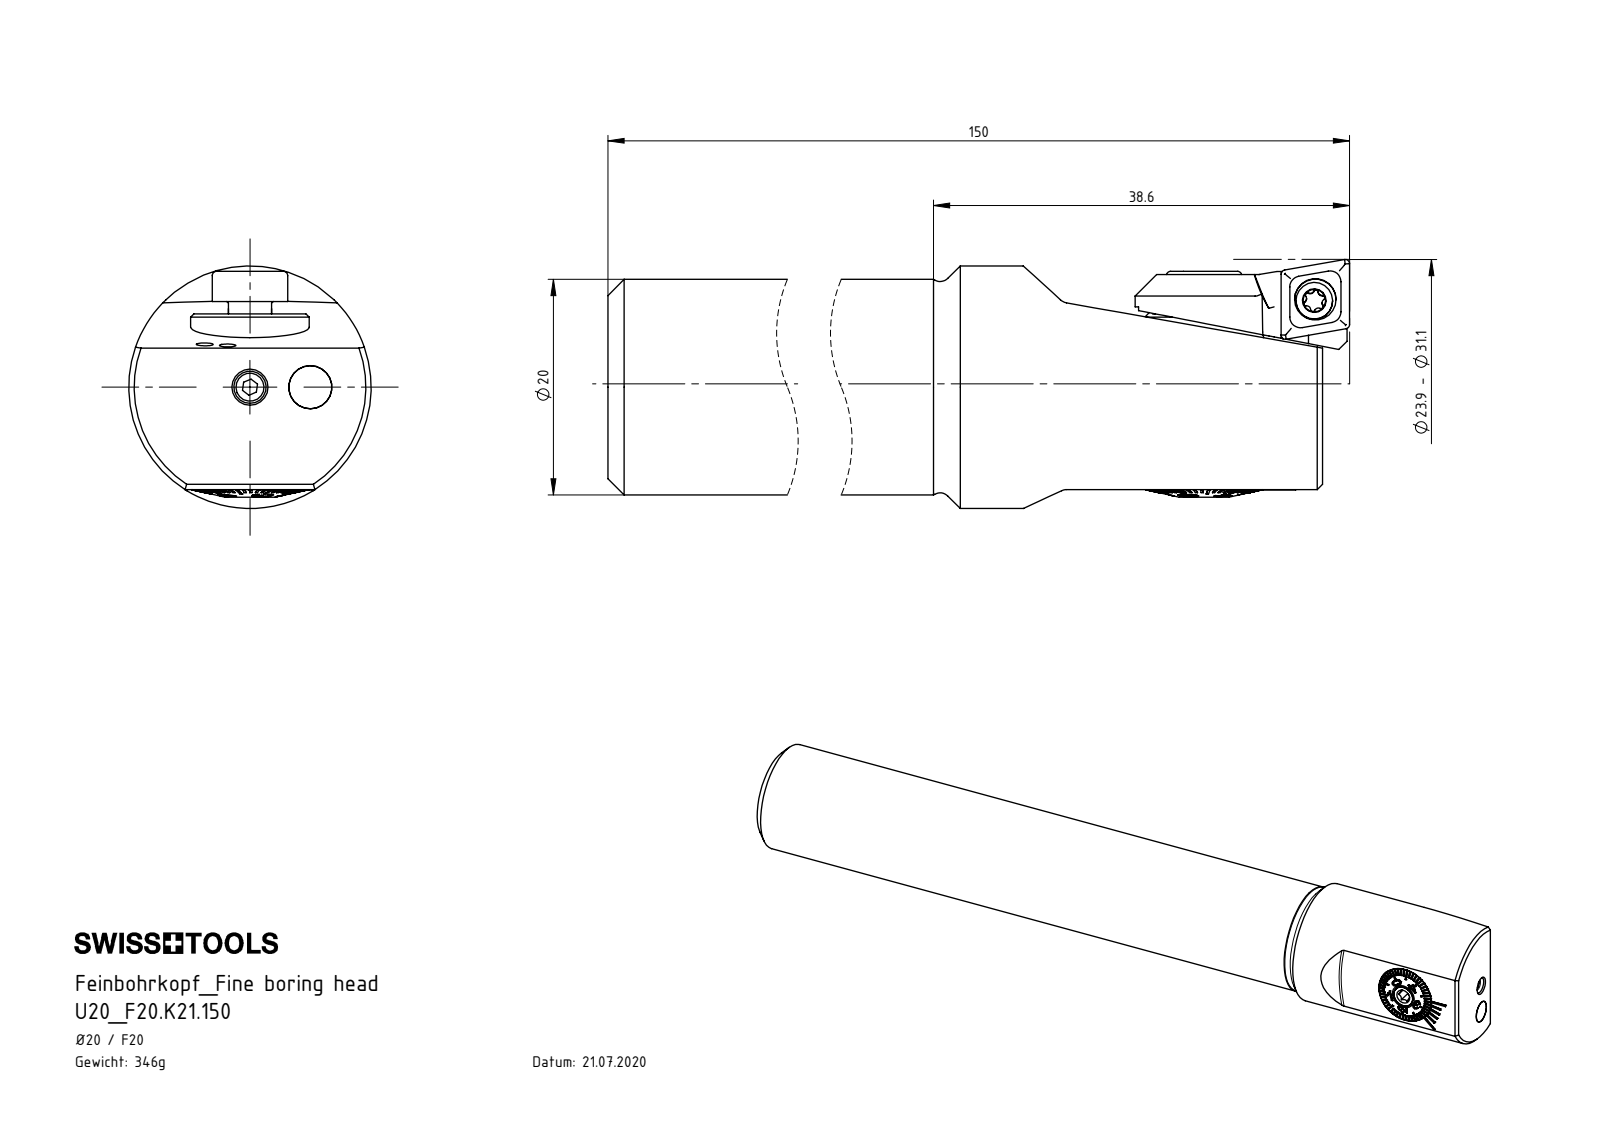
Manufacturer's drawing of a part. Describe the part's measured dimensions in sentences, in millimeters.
The part is named "DIN 3771 - 11x1_x; F20-WCA.001.005; F20-BG2.008.009_A; DIN 7984 - M4 x 6_PreviewCfg (+8 more)". Its 3-D file was written by "SolidWorks 2022 (AUTOMOTIVE_DESIGN)". It is 16 solids with 760 faces: 324 planar, 145 cylindrical and 291 other. Overall it measures 150 by 23.1 by 22.5 millimeters. Its volume is 44 816 cubic millimeters and its surface area 16 541 square millimeters. Round holes: 4 of diameter 2.1, 2 of diameter 1.5, 2 of diameter 3, 2 of diameter 3.3, 1 of diameter 1.08, 1 of diameter 1.9, 1 of diameter 2.05, 1 of diameter 2.8, 1 of diameter 3.85, 1 of diameter 4, 1 of diameter 4.5, 1 of diameter 5. Round bosses or shafts: 2 of diameter 4, 2 of diameter 3.95, 1 of diameter 22.5, 1 of diameter 20, 1 of diameter 10.98, 1 of diameter 10.85, 1 of diameter 8.65, 1 of diameter 7. Partial cylindrical surfaces (rounded edges, fillets, slot ends): 6 of radius 0.21, 4 of radius 0.36, 2 of radius 0.3, 2 of radius 0.36, 2 of radius 0.5, 2 of radius 1.25, 2 of radius 2, 2 of radius 5. The main face-to-face distances are 147.5, 16.3, 3.7, 12.6, 1.5, 0.8, 2.9, 16.65, 2.8, 15.5. The hole center spacings are 5.38, 5.6, 8.71.
